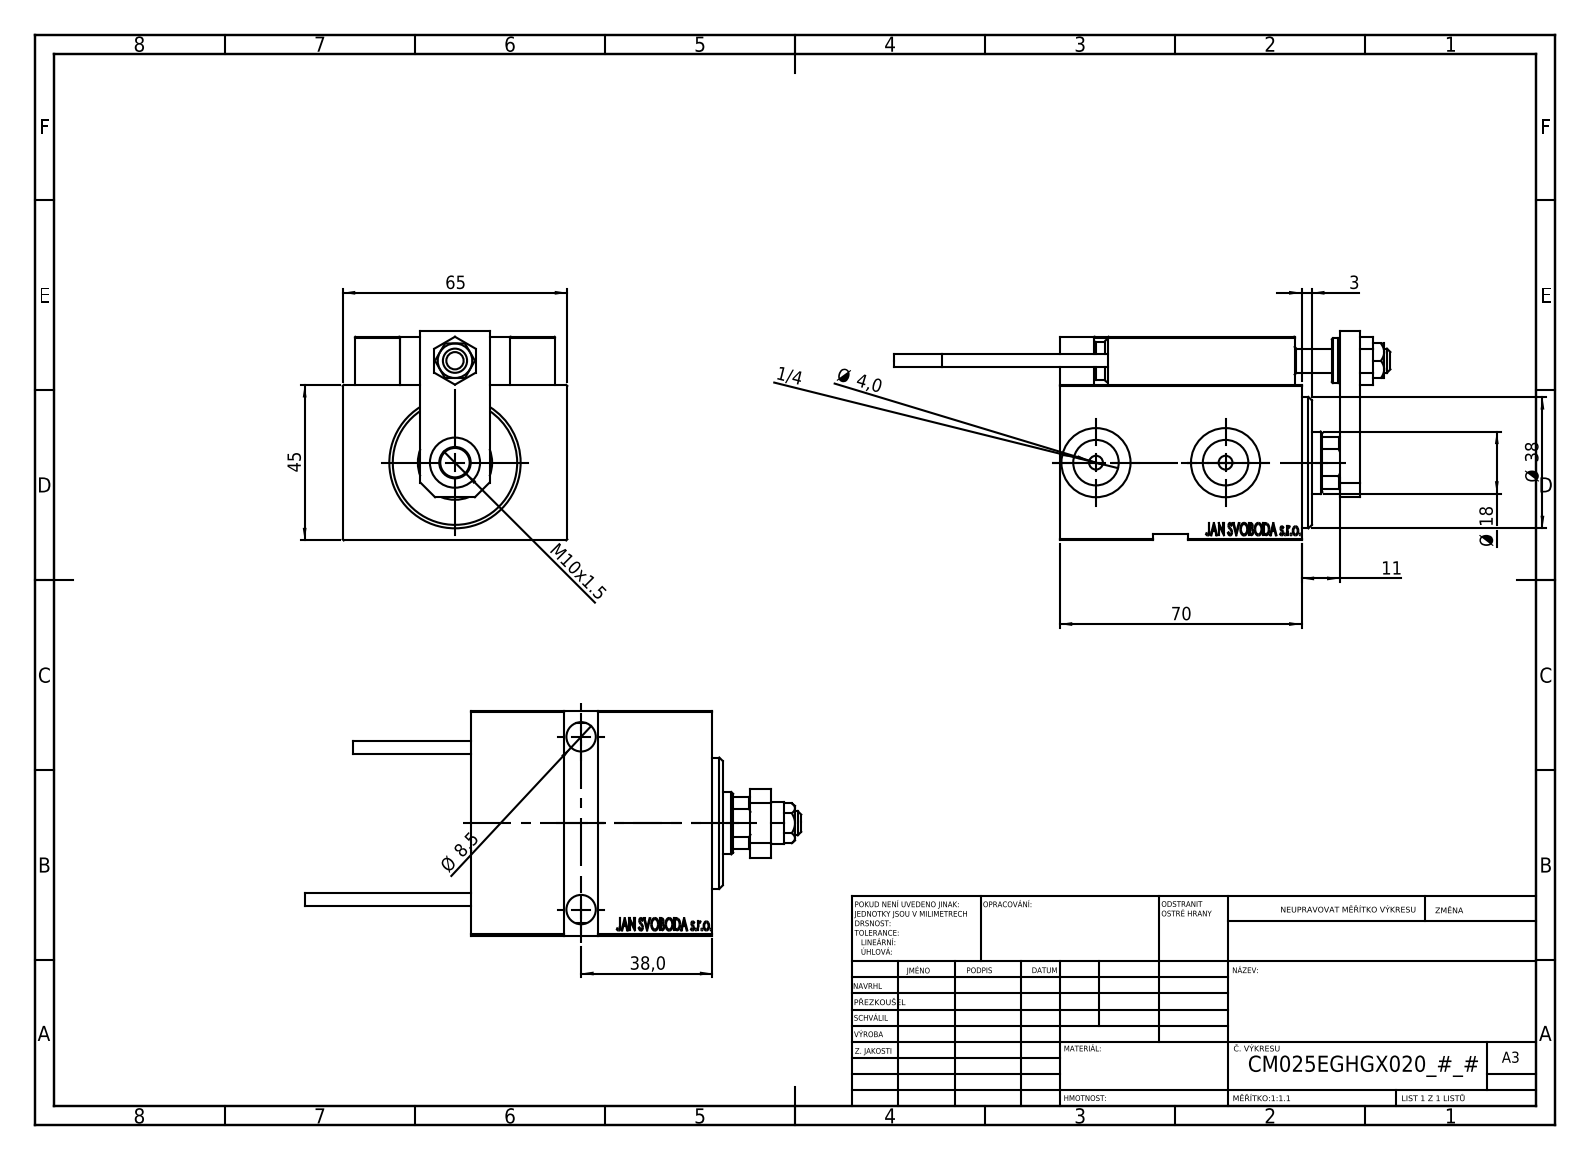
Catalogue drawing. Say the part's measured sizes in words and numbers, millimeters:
The part is named "NUT_D10; Block; SWITCH X; KONCOVKA (+7 more)". Its 3-D file was written by "SolidWorks 2019 (CONFIG_CONTROL_DESIGN)". It is 24 solids with 1283 faces: 568 planar, 174 cylindrical and 541 other. Overall it measures 143.7 by 65 by 60.5 millimeters. Its volume is 236 623 cubic millimeters and its surface area 63 468 square millimeters. Round holes: 6 of diameter 4, 5 of diameter 8, 4 of diameter 3.2, 3 of diameter 8.5, 2 of diameter 5, 2 of diameter 13.16, 2 of diameter 13.5, 2 of diameter 20, 1 of diameter 7, 1 of diameter 14.5, 1 of diameter 18, 1 of diameter 21.5. Round bosses or shafts: 2 of diameter 5, 2 of diameter 3.8, 1 of diameter 38, 1 of diameter 27, 1 of diameter 13, 1 of diameter 11. Partial cylindrical surfaces (rounded edges, fillets, slot ends): 30 of radius 0.3, 2 of radius 3, 1 of radius 8.5. The main face-to-face distances are 45, 65, 14, 59, 6, 19, 8, 70, 13, 3. The hole center spacings are 11.37, 20, 22.09, 29.59, 29.69, 30.89, 31.11, 34.17.
